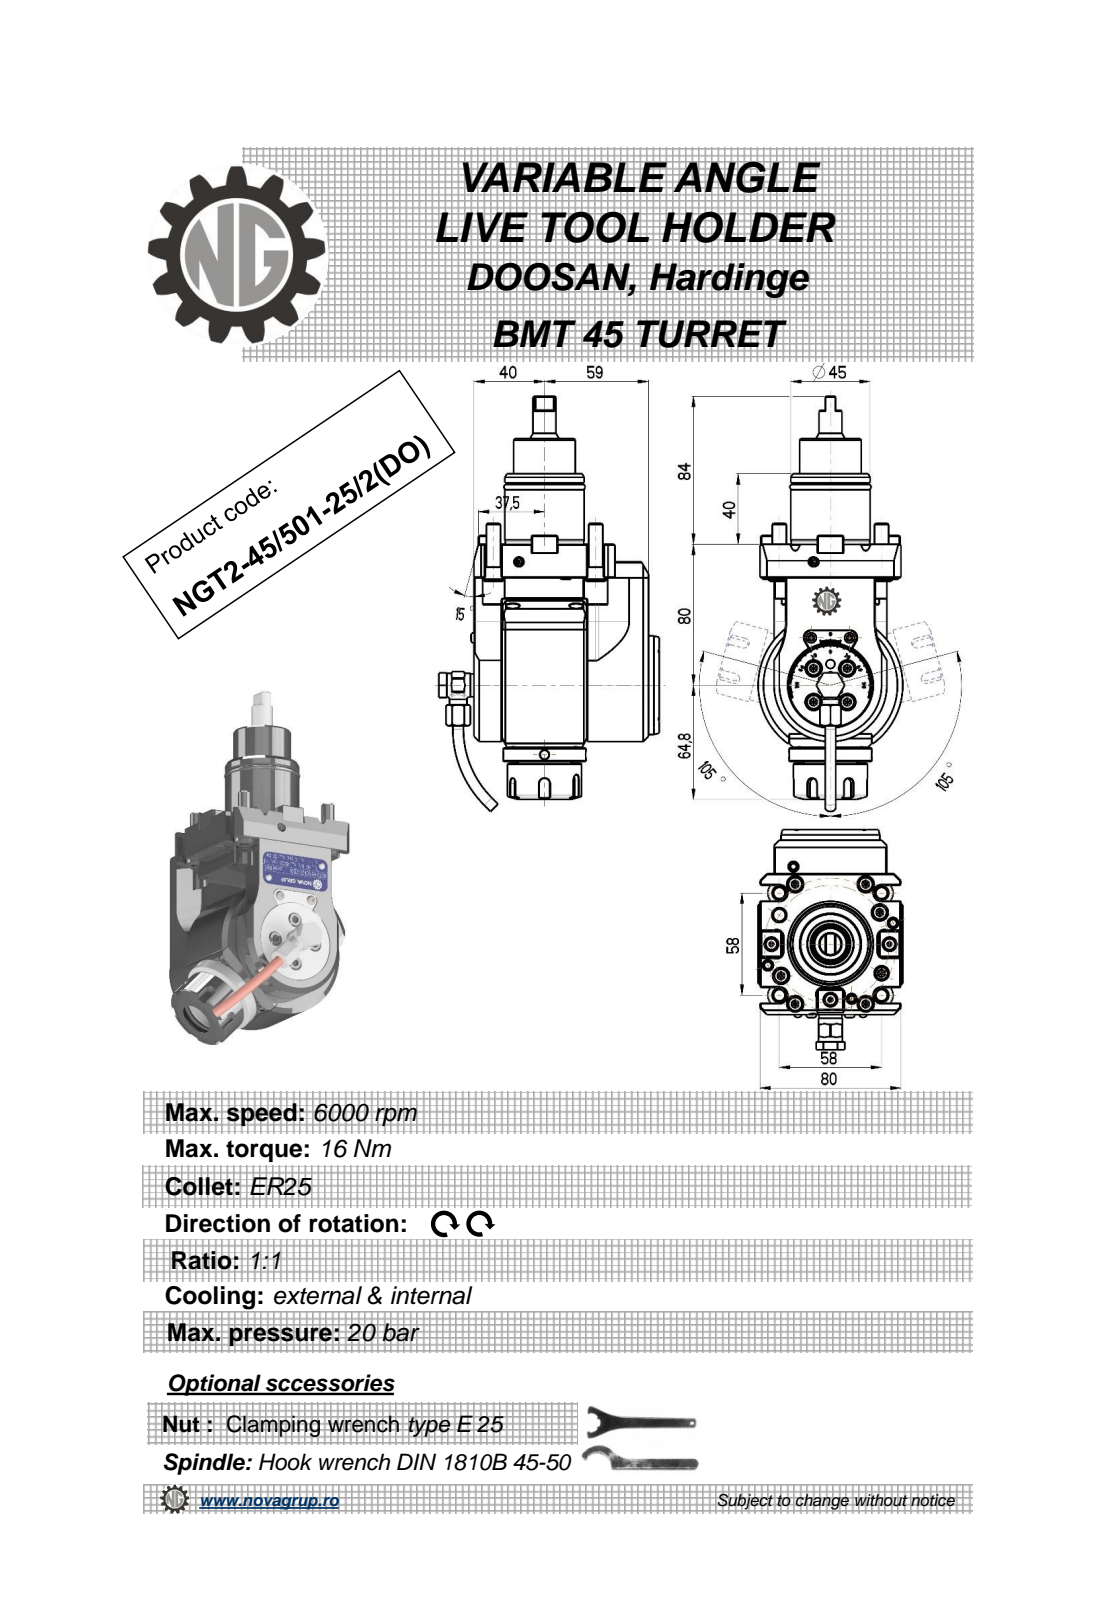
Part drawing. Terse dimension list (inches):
name: NGT2_45_501_25_2_DO
written by: PRO/ENGINEER BY PARAMETRIC TECHNOLOGY CORPORATION, 2010280 (CONFIG_CONTROL_DESIGN)
unit: in
bodies: 2 solids, 663 faces (299 planar, 170 cylindrical, 194 other)
size: 9.278 × 4.917 × 3.228
volume: 50.9 in³; area: 135.6 in²
holes: 3× ⌀0.157, 2× ⌀0.197, 2× ⌀0.268, 1× ⌀0.118, 1× ⌀0.244, 1× ⌀0.354, 1× ⌀0.433, 1× ⌀0.799, 1× ⌀1.654, 1× ⌀1.661
bosses: 6× ⌀0.512, 4× ⌀0.315, 4× ⌀0.236, 2× ⌀0.394, 2× ⌀0.224, 1× ⌀2.205, 1× ⌀1.85, 1× ⌀1.772
rounds: 20× R0.01, 5× R0.118, 4× R0.02, 4× R0.177, 4× R0.276, 2× R0.031, 2× R0.039, 2× R0.197
face distances: 2.52, 1.22, 0.315, 0.236, 3.898, 4.134, 0.63, 0.354, 0.748, 2.835
hole spacings: 1.314, 0.016, 1.553, 1.715, 1.727, 1.929, 1.945, 2.627
